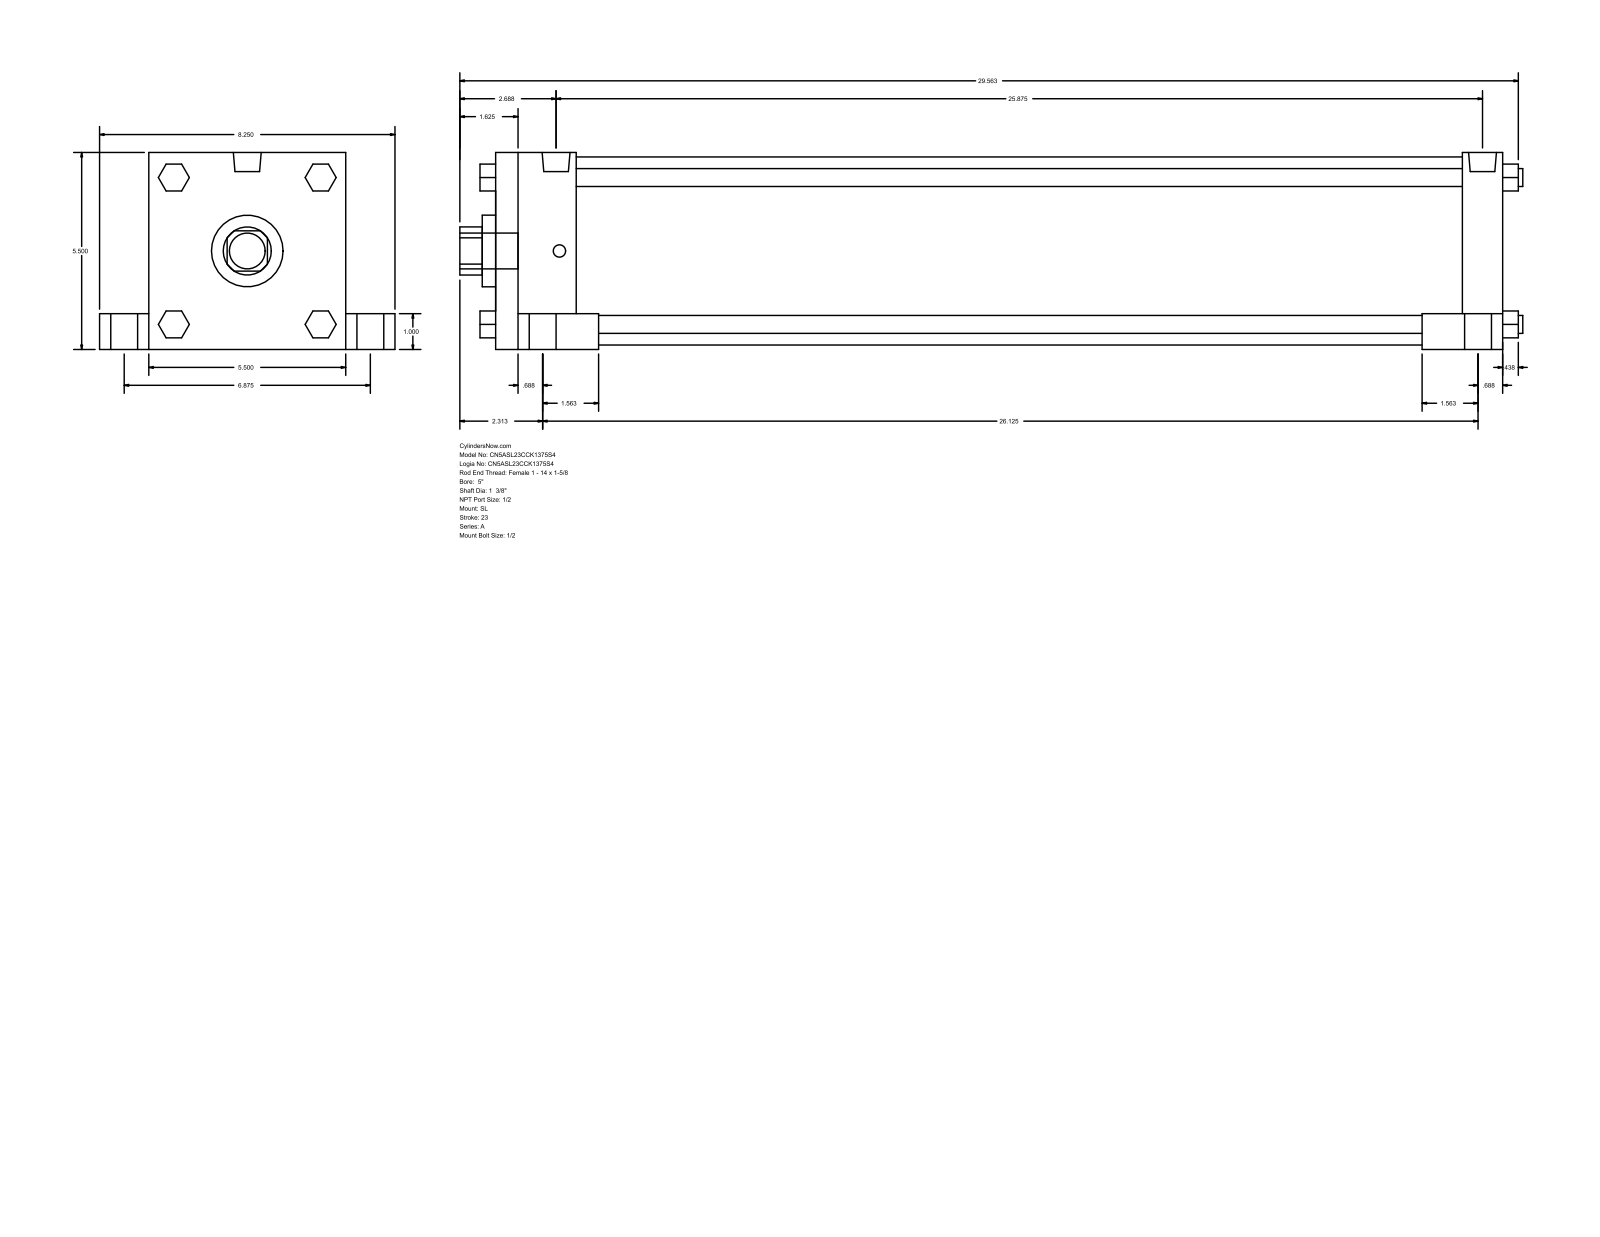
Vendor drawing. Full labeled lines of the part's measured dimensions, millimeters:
Part name (STEP PRODUCT): A_SL__0500_1.375
STEP written by: GSSL Pune (CONFIG_CONTROL_DESIGN)
Units: millimetres
Bodies: 0 solids, 150 faces (114 planar, 36 cylindrical, 0 other)
Overall size (bounding box): 754.06 × 209.55 × 139.7
Round holes (diameter × count): ⌀34.92 ×1, ⌀50.8 ×1, ⌀133.35 ×1
Round bosses / shafts (diameter × count): ⌀25.4 ×5, ⌀19.05 ×4, ⌀12.7 ×4, ⌀8.73 ×4, ⌀19.77 ×2
Partial cylindrical surfaces — rounded edges, fillets, slot ends (radius × count): R17.06 ×1
Main face-to-face distances: 139.7, 714.37, 57.15, 657.22, 25.4, 114.3, 34.93, 174.63, 28.57, 685.8
